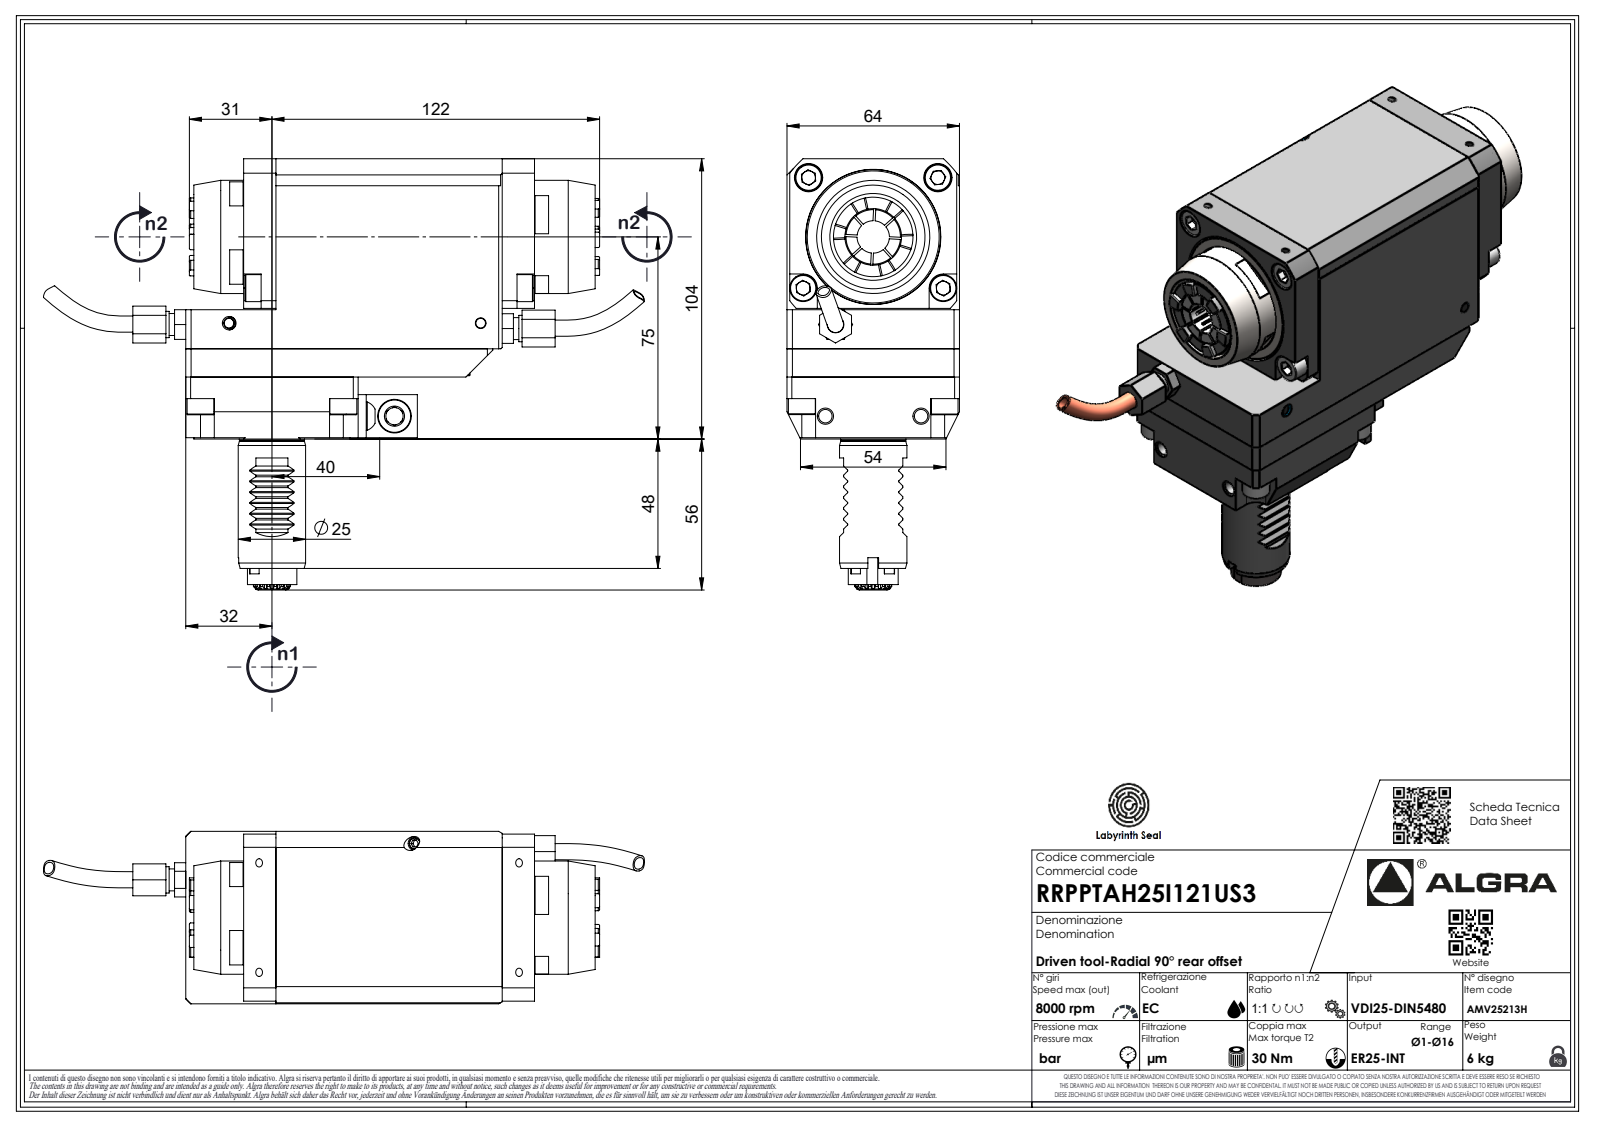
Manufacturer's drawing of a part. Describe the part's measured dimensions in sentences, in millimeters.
The part is named "RRPPTAH25I121US3". Its 3-D file was written by "SolidWorks 2023 (AUTOMOTIVE_DESIGN)". It is 1 solid with 761 faces: 515 planar, 116 cylindrical and 130 other. Overall it measures 223.12 by 160 by 64 millimeters. Its volume is 743 544 cubic millimeters and its surface area 68 145 square millimeters. Round holes: 1 of diameter 2.1, 1 of diameter 9, 1 of diameter 18.7, 1 of diameter 22. Round bosses or shafts: 2 of diameter 9.8, 2 of diameter 8.15, 1 of diameter 42, 1 of diameter 25, 1 of diameter 24.1, 1 of diameter 18.5, 1 of diameter 11, 1 of diameter 6.37. Partial cylindrical surfaces (rounded edges, fillets, slot ends): 12 of radius 0.3, 7 of radius 0.33, 7 of radius 0.52, 7 of radius 3.7, 2 of radius 5.25, 1 of radius 0.21, 1 of radius 6.15, 1 of radius 6.92. The main face-to-face distances are 64, 104, 48, 25, 81, 23, 1, 63, 56, 0.5. The hole center spacings are 40.
